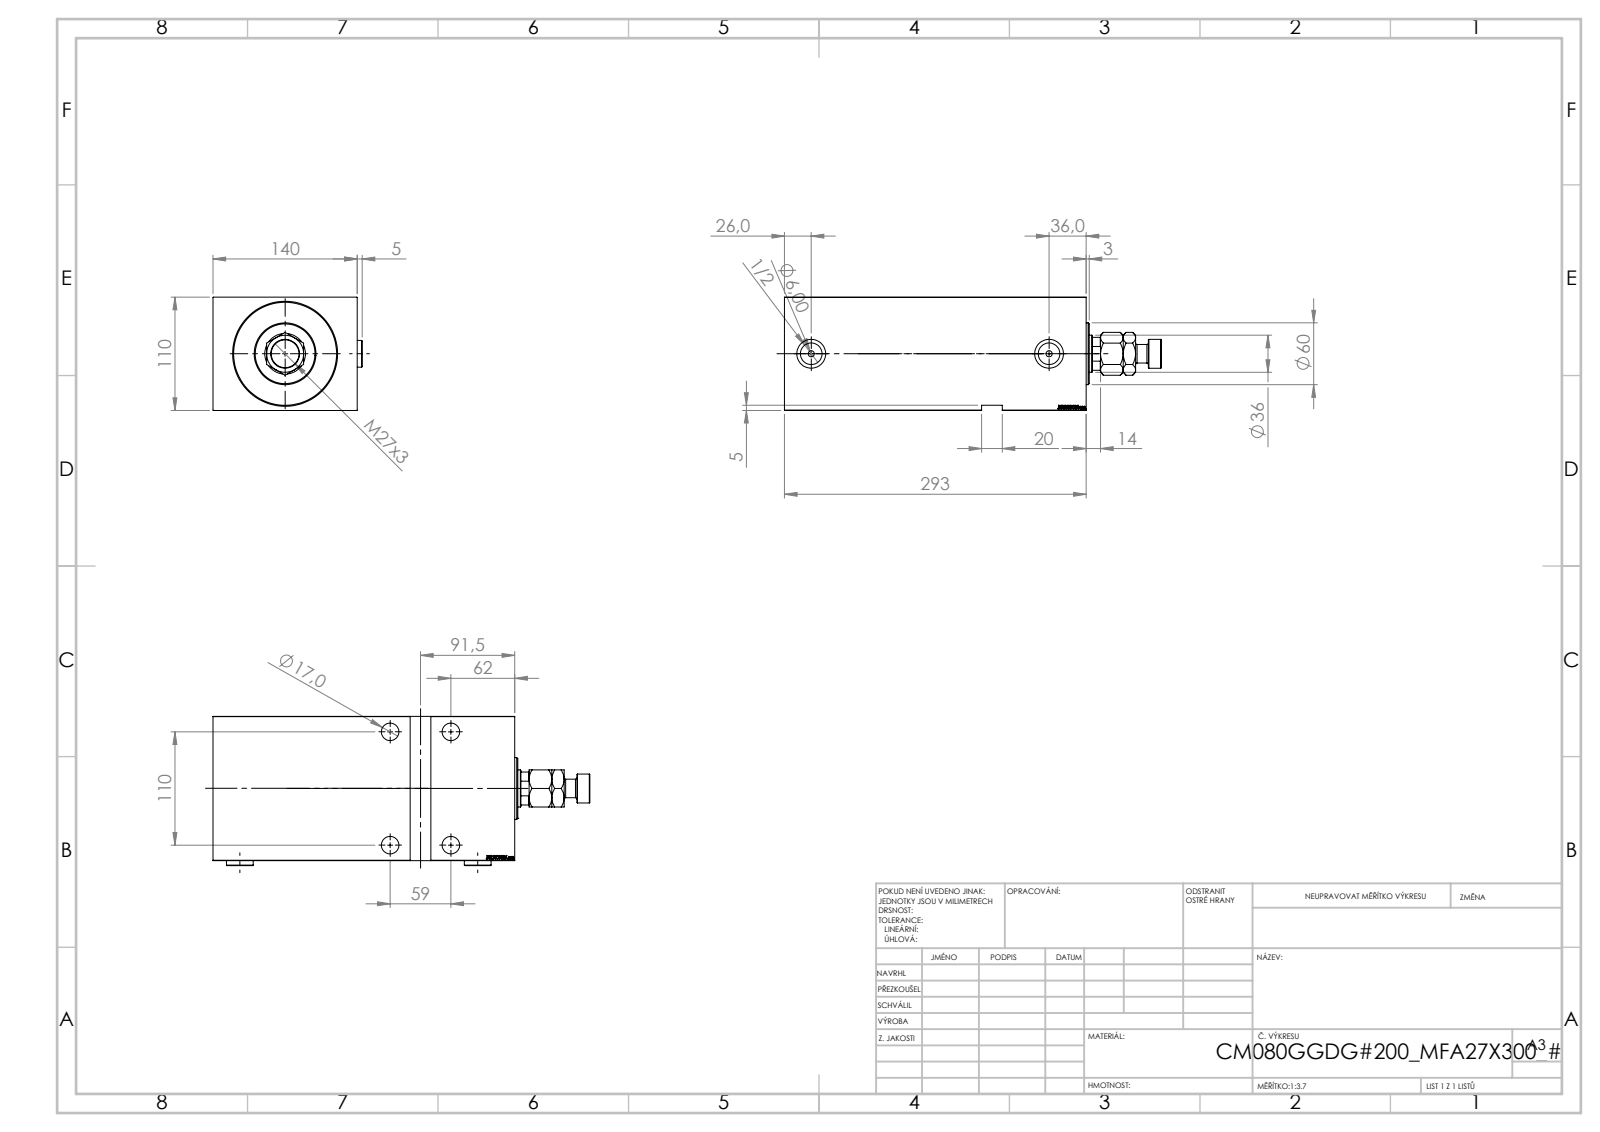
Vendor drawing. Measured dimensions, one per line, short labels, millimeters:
name: V450CM_VC_G; MFA; V450CM_G_VCP; V450CM_G_Body (+1 more)
written by: SolidWorks 2019 (CONFIG_CONTROL_DESIGN)
unit: mm
bodies: 6 solids, 964 faces (462 planar, 72 cylindrical, 430 other)
size: 366 × 144.9 × 110
volume: 3 565 000 mm³; area: 357 004 mm²
holes: 4× ⌀17, 4× ⌀25, 2× ⌀6, 2× ⌀20.96, 2× ⌀28, 1× ⌀25.5, 1× ⌀36, 1× ⌀39.5, 1× ⌀80, 1× ⌀82, 1× ⌀100
bosses: 2× ⌀26, 1× ⌀60, 1× ⌀28, 1× ⌀18
rounds: 1× R17.5
face distances: 110, 140, 5, 293, 21, 272, 288, 267, 79, 58
hole spacings: 59, 110, 124.82, 231
